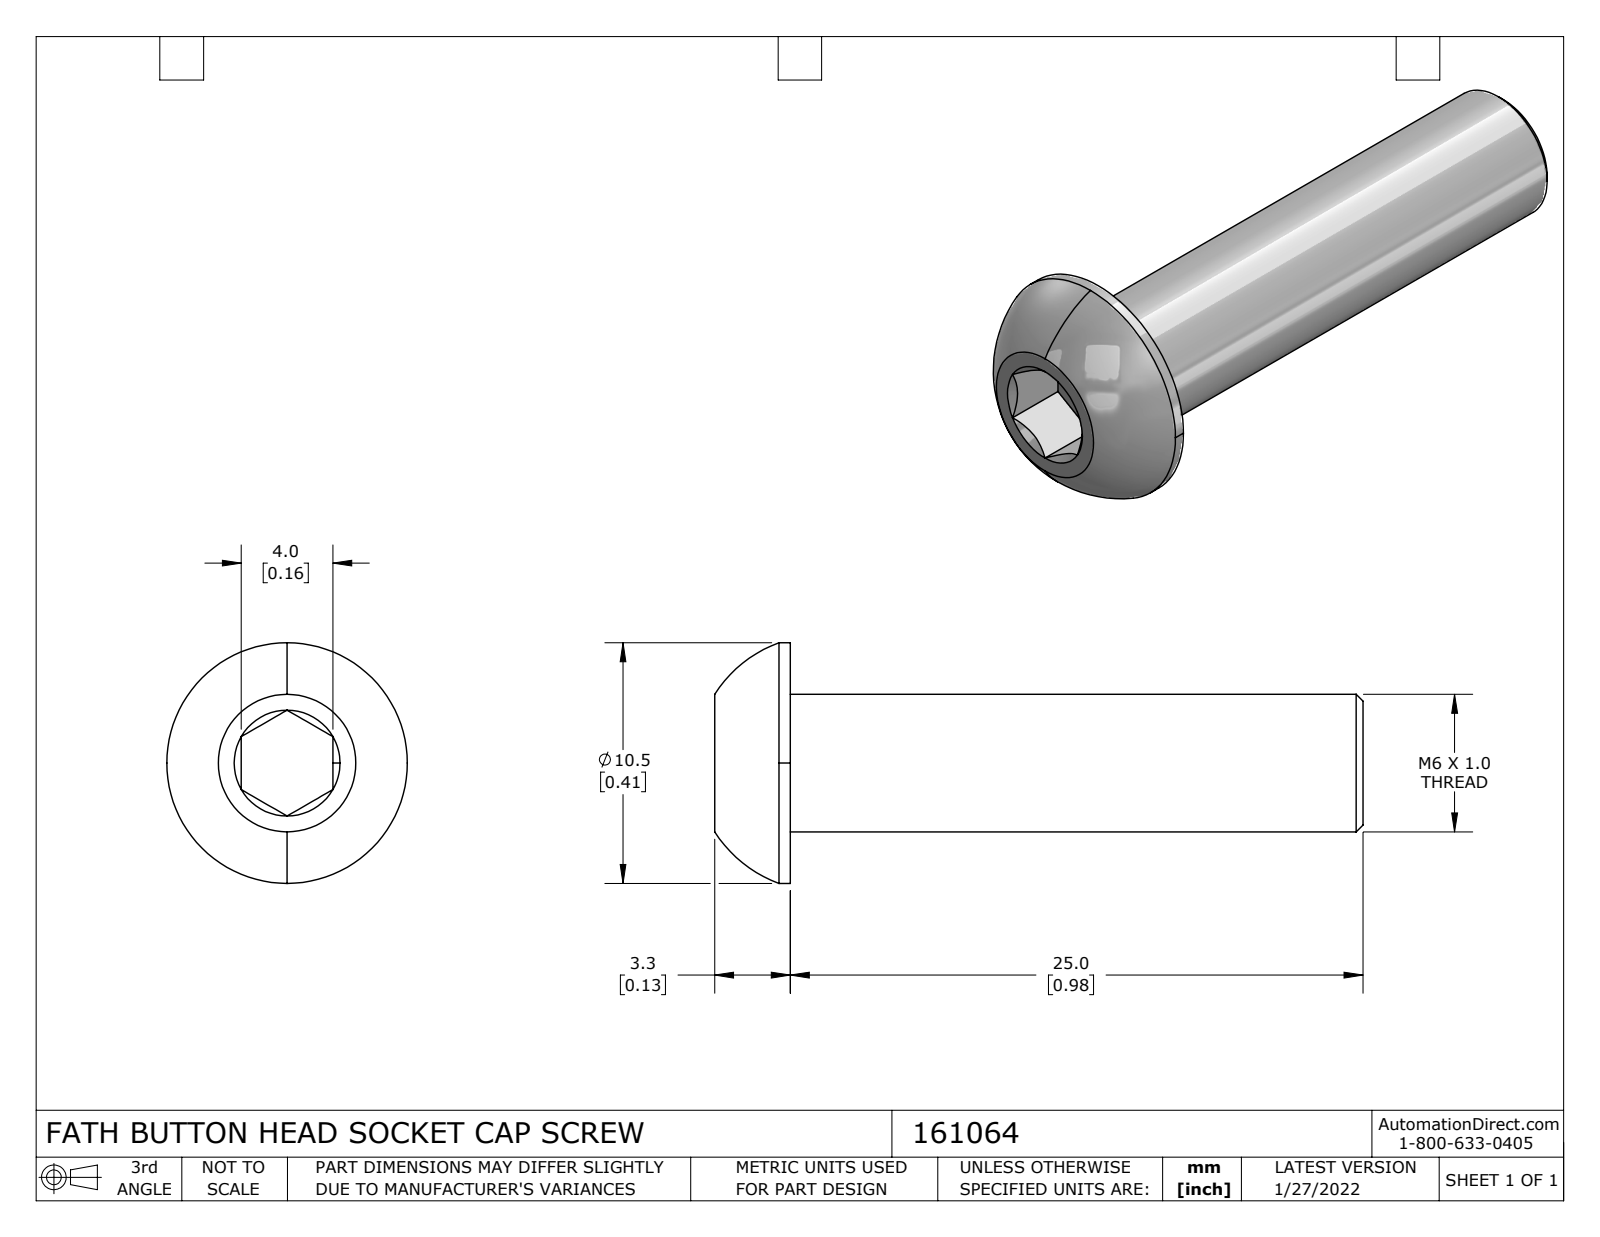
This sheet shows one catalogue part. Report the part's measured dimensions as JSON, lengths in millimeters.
{"part_name": "161064", "step_written_by": "SolidWorks 2021 (CONFIG_CONTROL_DESIGN)", "units": "millimeters", "bodies": {"solids": 1, "faces": 25, "planar": 10, "cylindrical": 4, "other": 11}, "overall_size": [28.3, 10.5, 10.5], "volume_mm3": 882, "surface_area_mm2": 735, "round_bosses_or_shafts": [[10.5, 1], [6, 1]], "face_to_face_distances": [25, 4, 25.5, 0.5, 28.3, 3.3, 2.8]}
